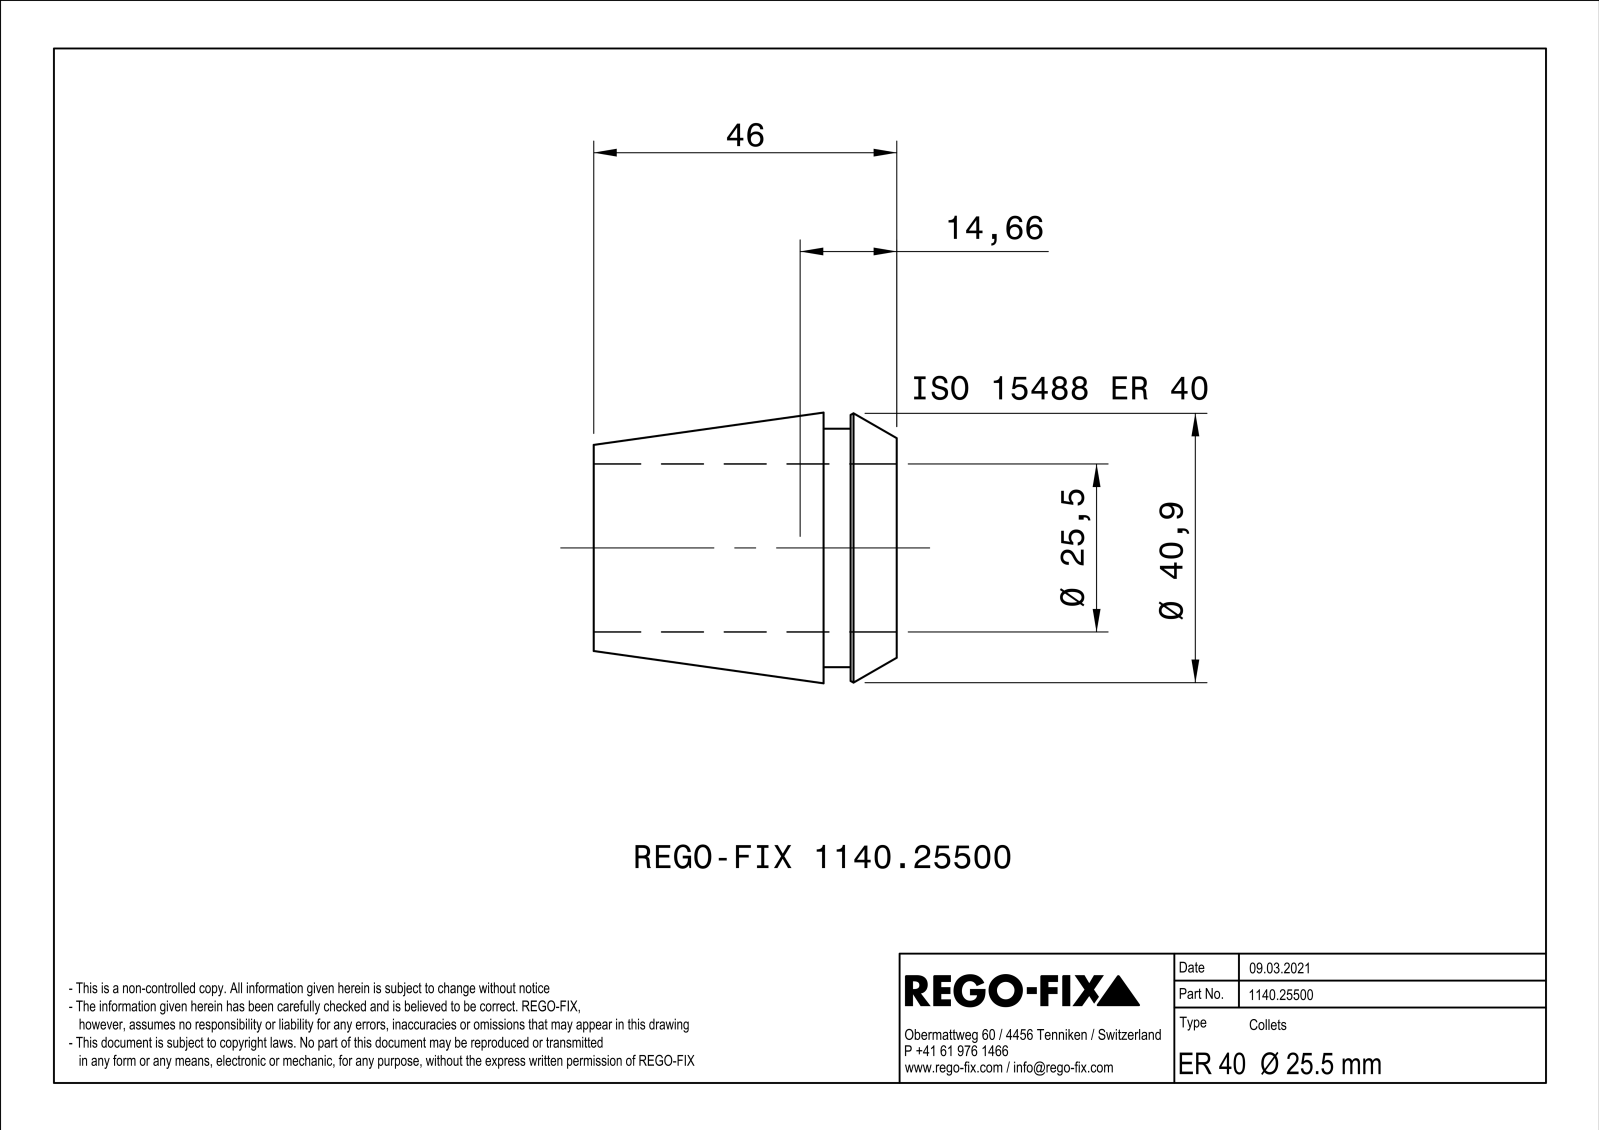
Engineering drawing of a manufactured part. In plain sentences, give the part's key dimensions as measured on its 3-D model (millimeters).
The part is named "NOCUT". Its 3-D file was written by "SIEMENS PLM Software Solid Edge ST10 (AUTOMOTIVE_DESIGN)". It is 1 solid with 177 faces: 88 planar, 9 cylindrical and 80 other. Overall it measures 46 by 40.99 by 40.99 millimeters. Its volume is 20 808 cubic millimeters and its surface area 15 912 square millimeters. Round holes: 1 of diameter 25.5. Round bosses or shafts: 1 of diameter 36.2. The main face-to-face distances are 1, 11.1, 7, 4.1, 46, 39, 34.9, 7.5, 0.5, 3.6.
